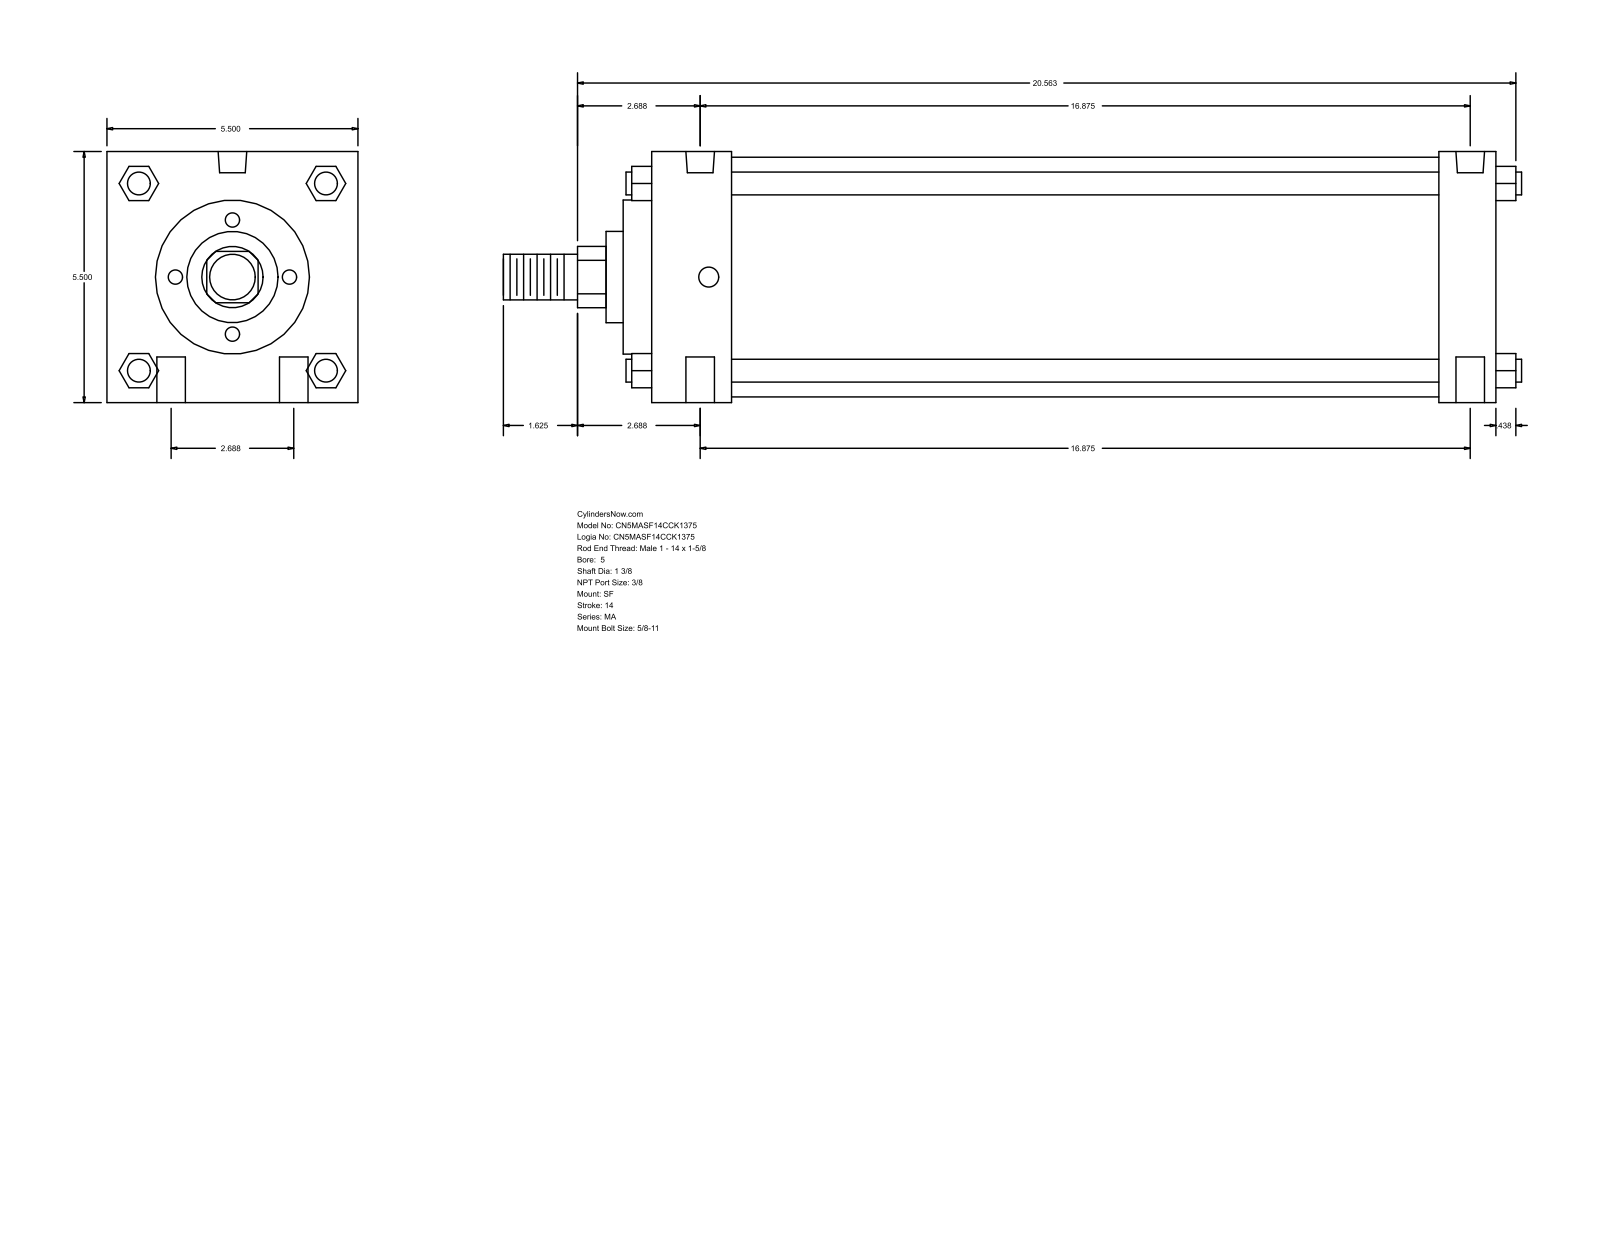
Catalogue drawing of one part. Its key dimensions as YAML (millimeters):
part_name: "MA_SF__0500_1.375"
step_written_by: "GSSL Pune (CONFIG_CONTROL_DESIGN)"
units: millimeters
bodies: {solids: 0, faces: 126, planar: 95, cylindrical: 31, other: 0}
overall_size: [566.74, 139.7, 139.7]
round_holes:
  - {diameter: 15.88, count: 4}
  - {diameter: 11.11, count: 2}
  - {diameter: 15.93, count: 2}
round_bosses_or_shafts:
  - {diameter: 12.7, count: 4}
  - {diameter: 133.35, count: 1}
  - {diameter: 85.72, count: 1}
  - {diameter: 50.8, count: 1}
  - {diameter: 34.92, count: 1}
  - {diameter: 25.4, count: 1}
partial_cylinders:
  - {radius: 17.06, count: 1}
face_to_face_distances: [139.7, 469.91, 44.45, 438.16, 393.71, 425.46, 31.75, 15.87, 60.32, 454.03]
hole_center_spacings: [34.13, 429.99, 428.63, 68.26, 434.03, 419.09]
